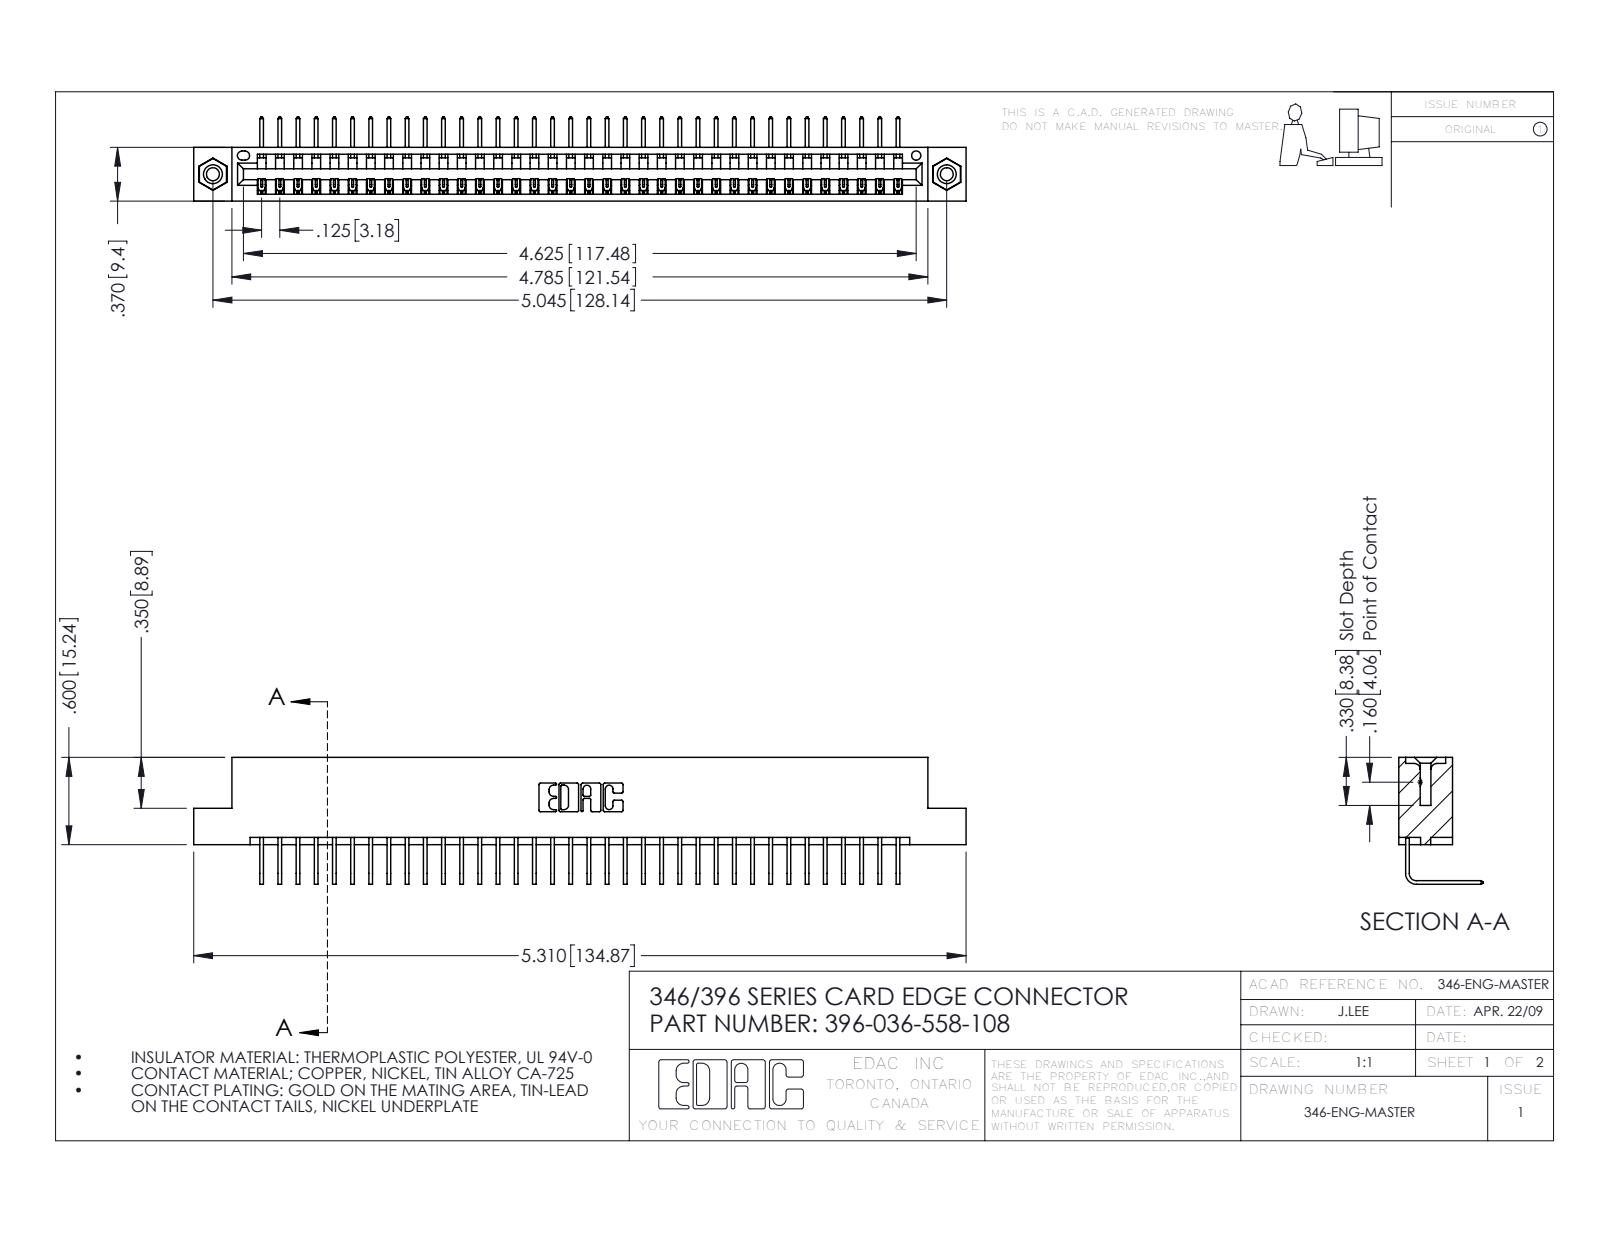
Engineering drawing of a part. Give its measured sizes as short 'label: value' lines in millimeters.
name: 346 Part_Flush Mounting Lugs - 0.156 Dia-TI; 396-036-558-108; 345-292-001_558 Tail - 2; 345-250-001_345-250-003-102
written by: SolidWorks 2016 (CONFIG_CONTROL_DESIGN)
unit: mm
bodies: 39 solids, 2342 faces (1620 planar, 706 cylindrical, 16 other)
size: 134.9 × 22.2 × 14.7
volume: 13 000 mm³; area: 16 900 mm²
holes: 2× ⌀2.3, 2× ⌀3.2, 2× ⌀4, 1× ⌀1.6
bosses: 2× ⌀3.9
rounds: 72× R0.2, 22× R0.3, 6× R0.2, 6× R0.8, 3× R0.7, 2× R0.8, 2× R1, 1× R0.4
face distances: 8.2, 1.2, 9.4, 6.4, 7.6, 0.6, 1.8, 3.8, 5.6, 2.5
hole spacings: 6.2, 122.8, 128.1
